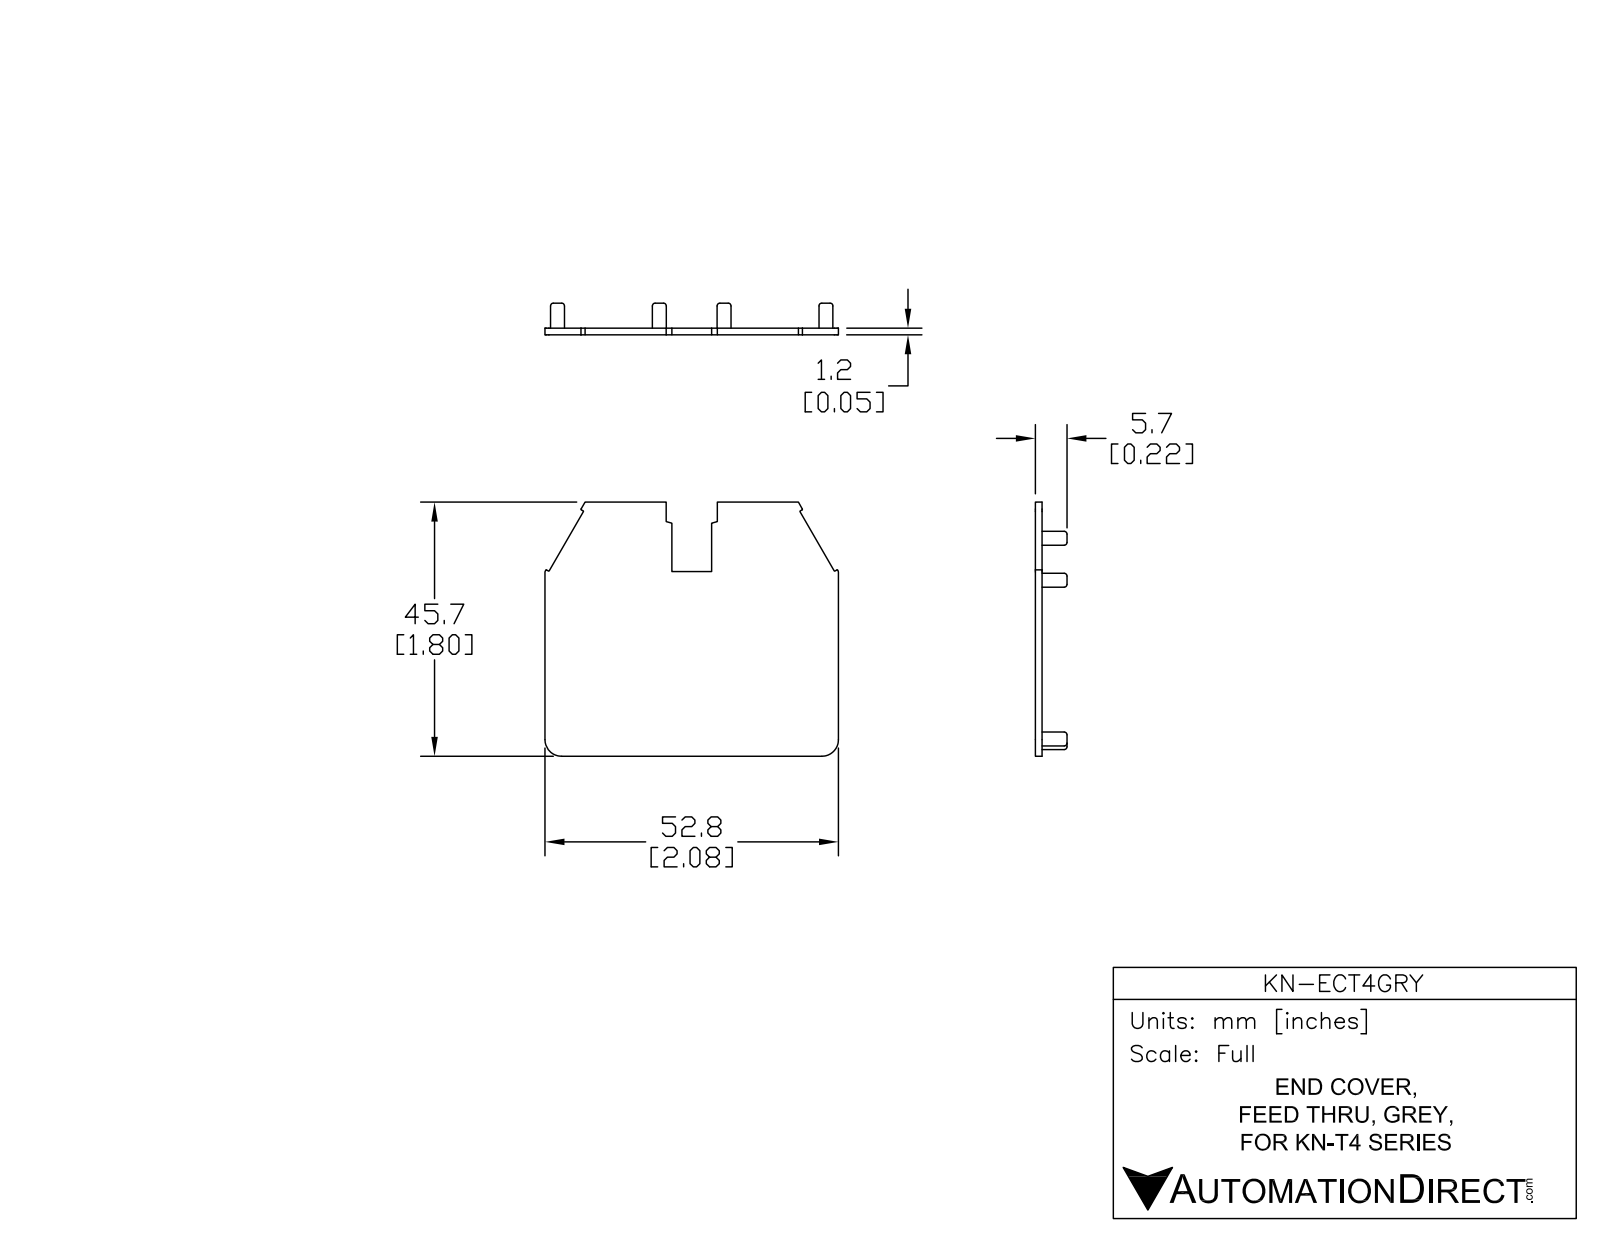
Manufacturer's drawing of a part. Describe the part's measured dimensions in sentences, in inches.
The part is named "KN-ECT4GRY". Its 3-D file was written by "SolidWorks 2014 (AUTOMOTIVE_DESIGN)". It is 1 solid with 86 faces: 36 planar, 38 cylindrical and 12 other. Overall it measures 2.079 by 1.8 by 0.224 inches. Its volume is 0.168 cubic inches and its surface area 7.68 square inches. Round holes: 6 of diameter 0.039. Round bosses or shafts: 6 of diameter 0.098. Partial cylindrical surfaces (rounded edges, fillets, slot ends): 8 of radius 0.004, 2 of radius 0.012, 2 of radius 0.118. The main face-to-face distances are 0.047, 2.079, 1.8, 0.899, 1.18, 0.281, 1.308, 0.492, 0.858, 1.22. The hole center spacings are 1.902, 0.459, 0.78, 0.78, 1.124, 1.15, 1.217, 1.217.
